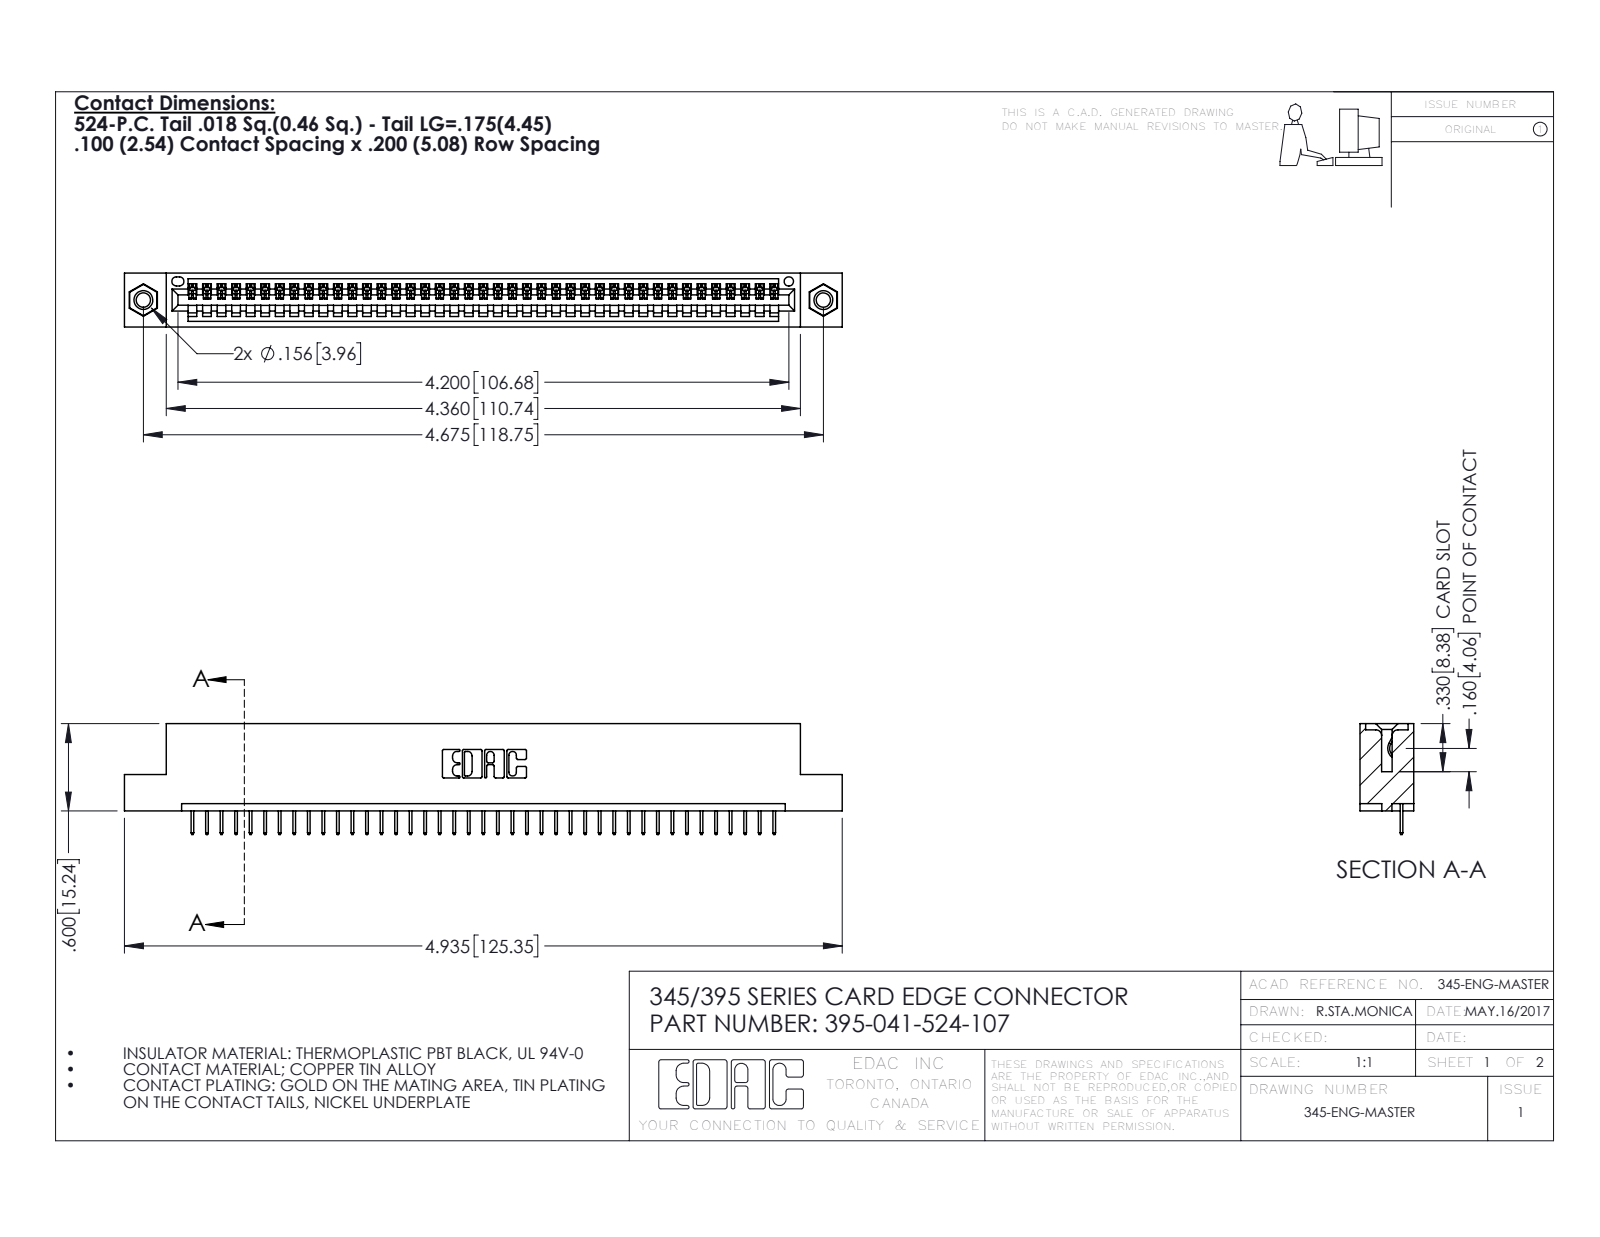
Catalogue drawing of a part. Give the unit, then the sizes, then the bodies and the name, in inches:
Units: inches
Overall size (bounding box): 4.935 × 0.762 × 0.37
Round holes (diameter × count): ⌀0.098 ×2, ⌀0.125 ×2, ⌀0.156 ×2, ⌀0.064 ×1
Round bosses / shafts (diameter × count): ⌀0.155 ×2
Partial cylindrical surfaces — rounded edges, fillets, slot ends (radius × count): R0.006 ×82, R0.01 ×22, R0.007 ×6, R0.031 ×6, R0.026 ×3, R0.031 ×2, R0.04 ×2, R0.014 ×1
Main face-to-face distances: 0.072, 0.298, 0.37, 0.2, 0.098, 0.272, 0.025, 0.225, 0.072, 0.149
Hole centre spacings: 0.27, 4.439, 4.675
Volume: 0.715 in³ · Surface area: 23.37 in²
Bodies: 44 solids, 2728 faces (1998 planar, 714 cylindrical, 16 other)
Part name (STEP PRODUCT): 395-041-524-107; 345-292-001_345-293-124; 345 Part_Flush Mounting Lugs - 0.156 Dia-TI; 345-250-001_345-250-005-103
STEP written by: SolidWorks 2016 (CONFIG_CONTROL_DESIGN)
